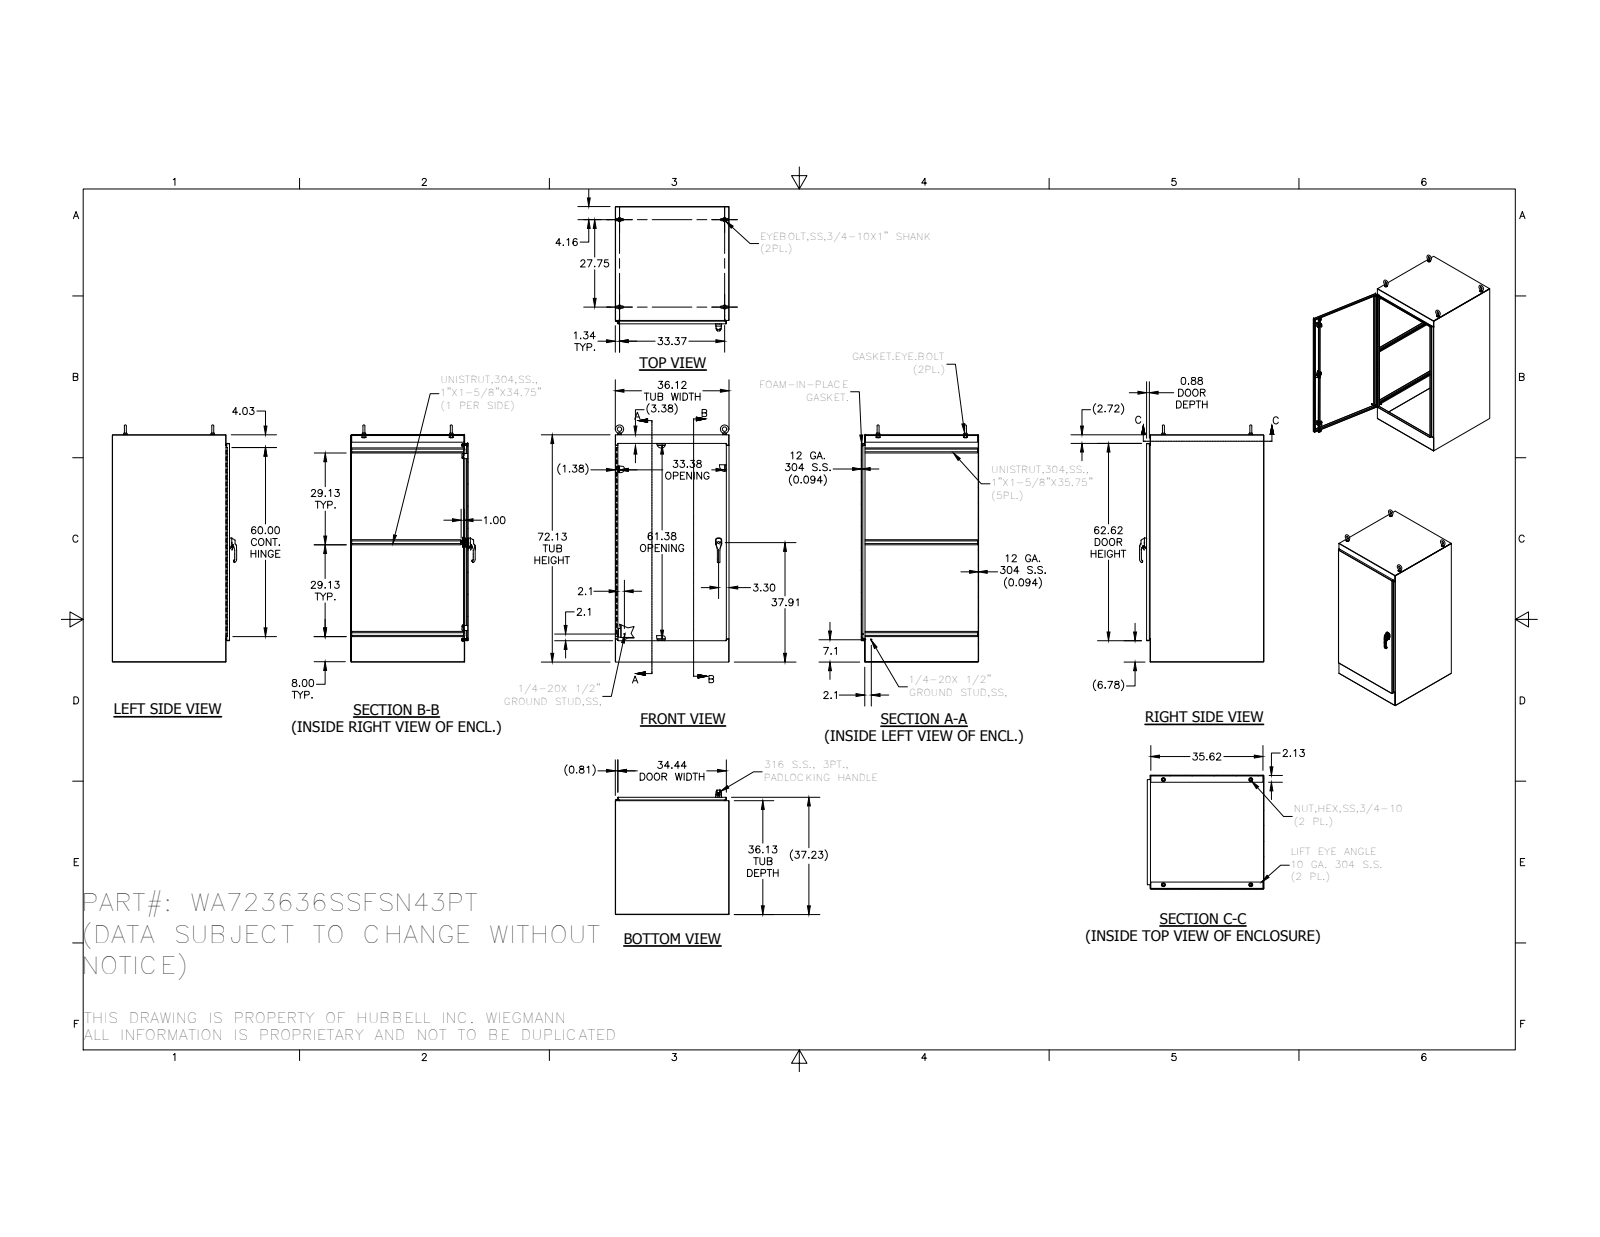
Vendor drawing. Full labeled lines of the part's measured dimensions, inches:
Part name (STEP PRODUCT): WA7236SSFSN43PT-RS; 7379-M6-8X25_AF0; SS_LARGE_DOOR_ROD_ASSM-37029; DIN3771_16X2_5 (+8 more)
STEP written by: SolidWorks 2014 (AUTOMOTIVE_DESIGN)
Units: inches
Bodies: 72 solids, 3771 faces (1252 planar, 1371 cylindrical, 1148 other)
Overall size (bounding box): 75.248 × 39.476 × 36.125
Volume: 1 470 in³ · Surface area: 30 467 in²
Round holes (diameter × count): ⌀0.262 ×8, ⌀0.375 ×8, ⌀0.187 ×4, ⌀0.642 ×4, ⌀0.813 ×4, ⌀0.813 ×4, ⌀0.213 ×3, ⌀0.25 ×3, ⌀0.28 ×3, ⌀0.165 ×2, ⌀0.241 ×2, ⌀0.252 ×2
Round bosses / shafts (diameter × count): ⌀1.25 ×4, ⌀1.12 ×4, ⌀0.75 ×4, ⌀1 ×3, ⌀0.236 ×3, ⌀0.563 ×2, ⌀0.533 ×2, ⌀0.531 ×2
Partial cylindrical surfaces — rounded edges, fillets, slot ends (radius × count): R0.02 ×180, R0.012 ×107, R0.125 ×26, R0.019 ×23, R0.05 ×19, R0.031 ×17, R0.079 ×14, R0.125 ×13
Main face-to-face distances: 0.094, 36.031, 37.133, 35.937, 36.125, 72.031, 37.039, 37.227, 71.937, 72.125
Hole centre spacings: 33.437, 6.667, 20, 0.38, 0.76, 1.102, 1.714, 2.763
